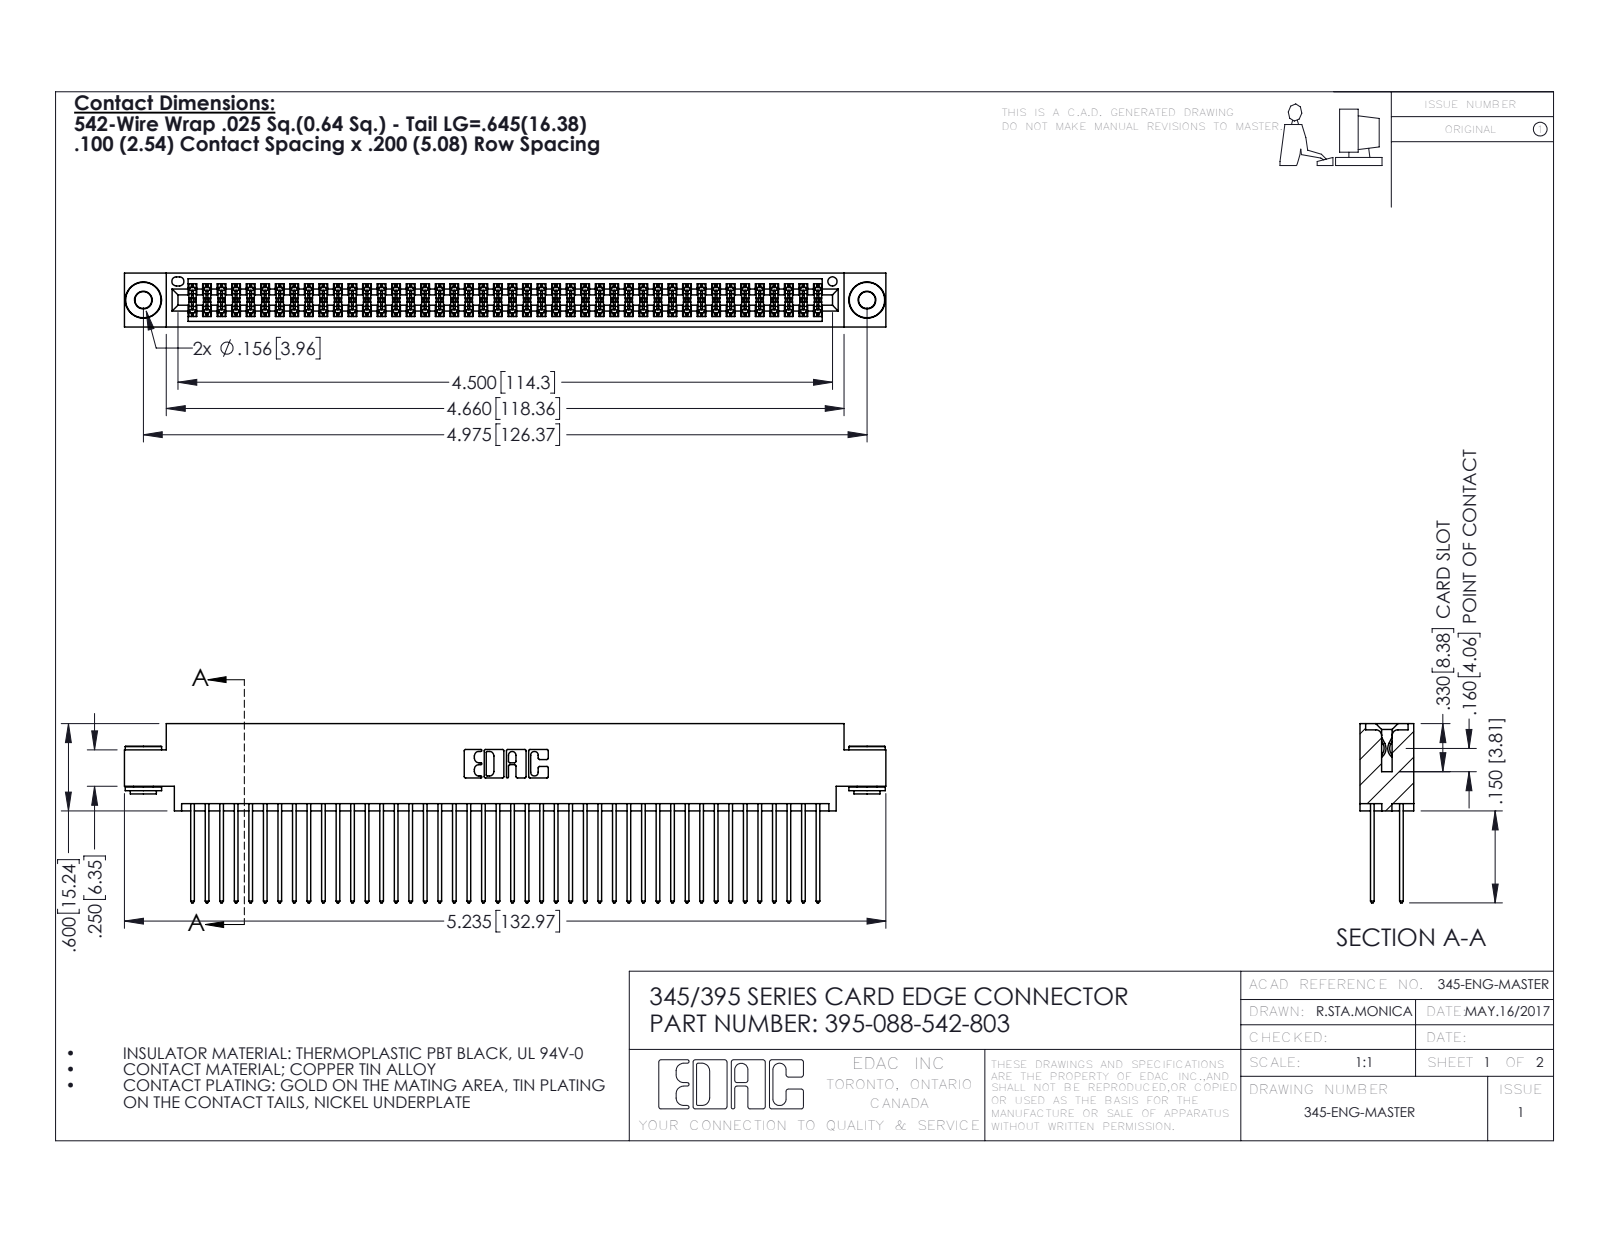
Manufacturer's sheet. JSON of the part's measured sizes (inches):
{"part_name": "395-088-542-803; 345-250-002_345-250-002-102; 345 Part_0.170 Offset - 0.156 Dia-TH; 345-292-001_345-293-142", "step_written_by": "SolidWorks 2016 (CONFIG_CONTROL_DESIGN)", "units": "inches", "bodies": {"solids": 91, "faces": 4568, "planar": 2998, "cylindrical": 1562, "other": 8}, "overall_size": [5.235, 1.232, 0.37], "volume_in3": 0.809, "surface_area_in2": 33.93, "round_holes": [[0.116, 2], [0.156, 2], [0.064, 1]], "round_bosses_or_shafts": [[0.25, 2], [0.18, 2], [0.136, 2]], "partial_cylinders_radius": [[0.006, 132], [0.01, 88], [0.01, 22], [0.007, 6], [0.031, 6], [0.026, 3], [0.014, 2], [0.019, 2]], "face_to_face_distances": [0.072, 0.298, 0.2, 0.098, 0.272, 0.025, 0.37, 0.225, 0.175, 0.149], "hole_center_spacings": [0.27, 4.739, 4.975]}
